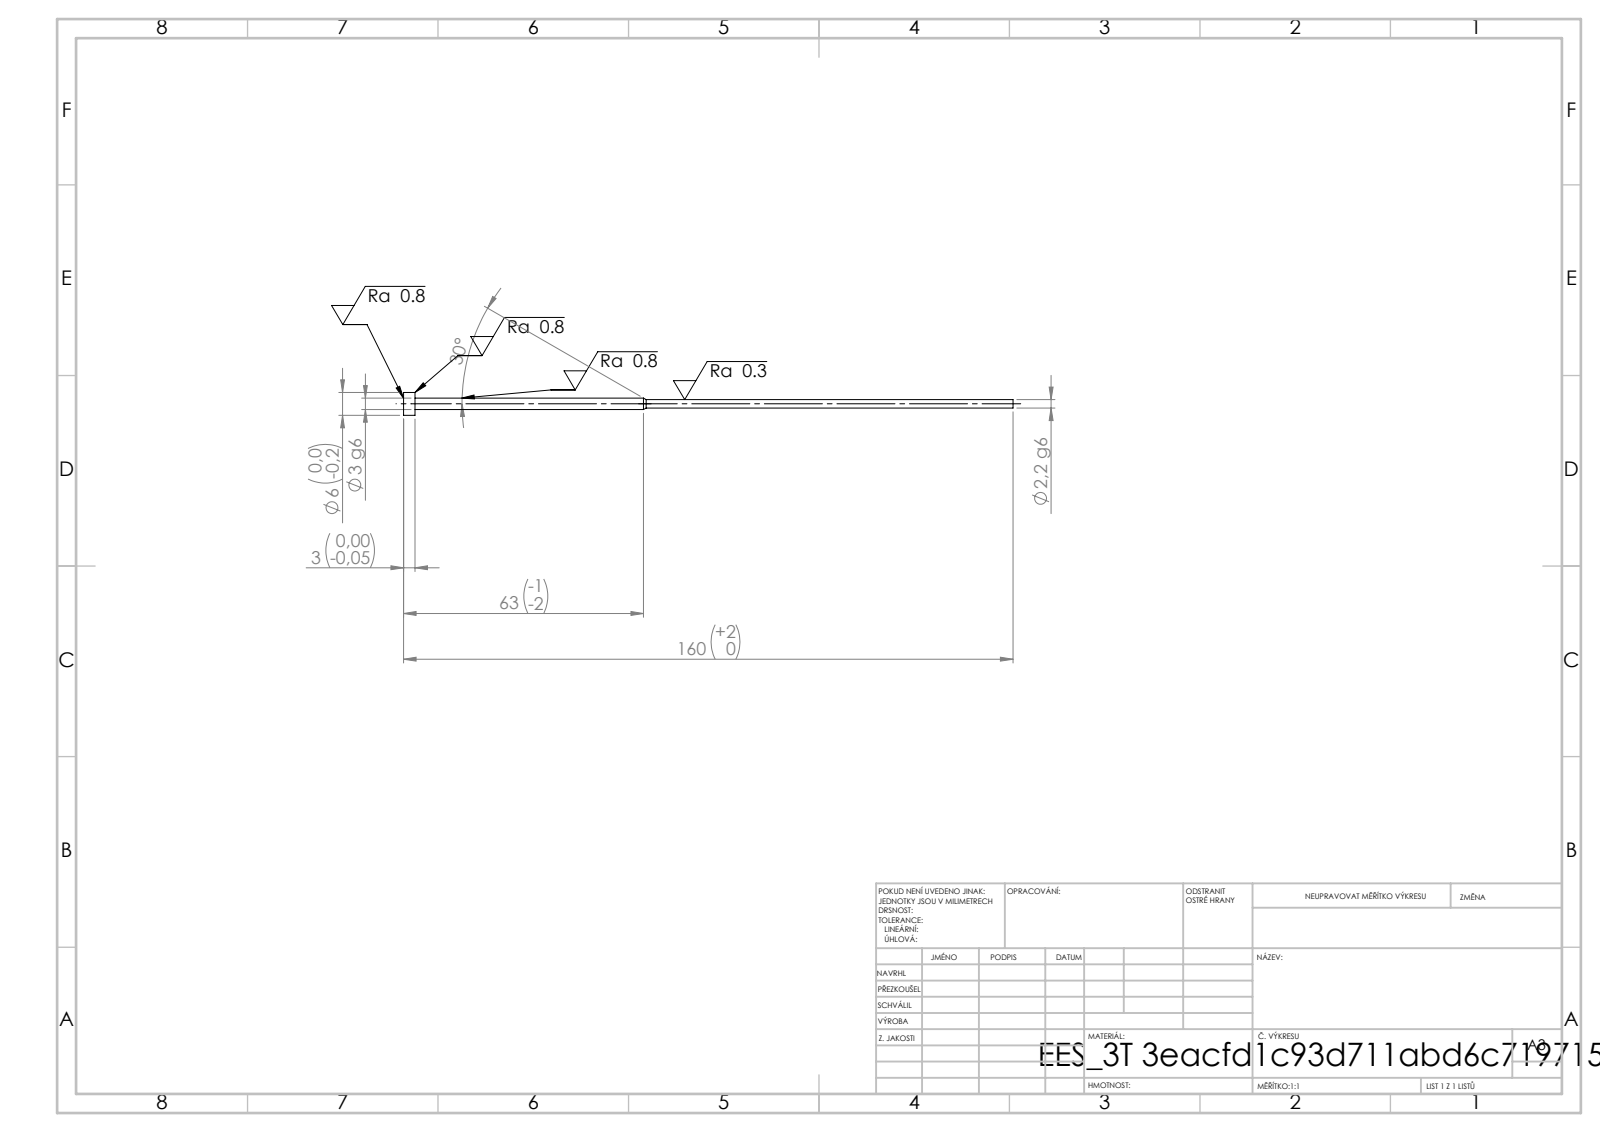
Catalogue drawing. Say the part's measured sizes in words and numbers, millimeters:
Its 3-D file was written by "SolidWorks 2019 (CONFIG_CONTROL_DESIGN)". It is 1 solid with 11 faces: 3 planar, 6 cylindrical and 2 other. Overall it measures 160 by 6 by 6 millimeters. Its volume is 879 cubic millimeters and its surface area 1 347 square millimeters. Round bosses or shafts: 1 of diameter 6, 1 of diameter 3, 1 of diameter 2.2. The main face-to-face distances are 3, 157, 160.
